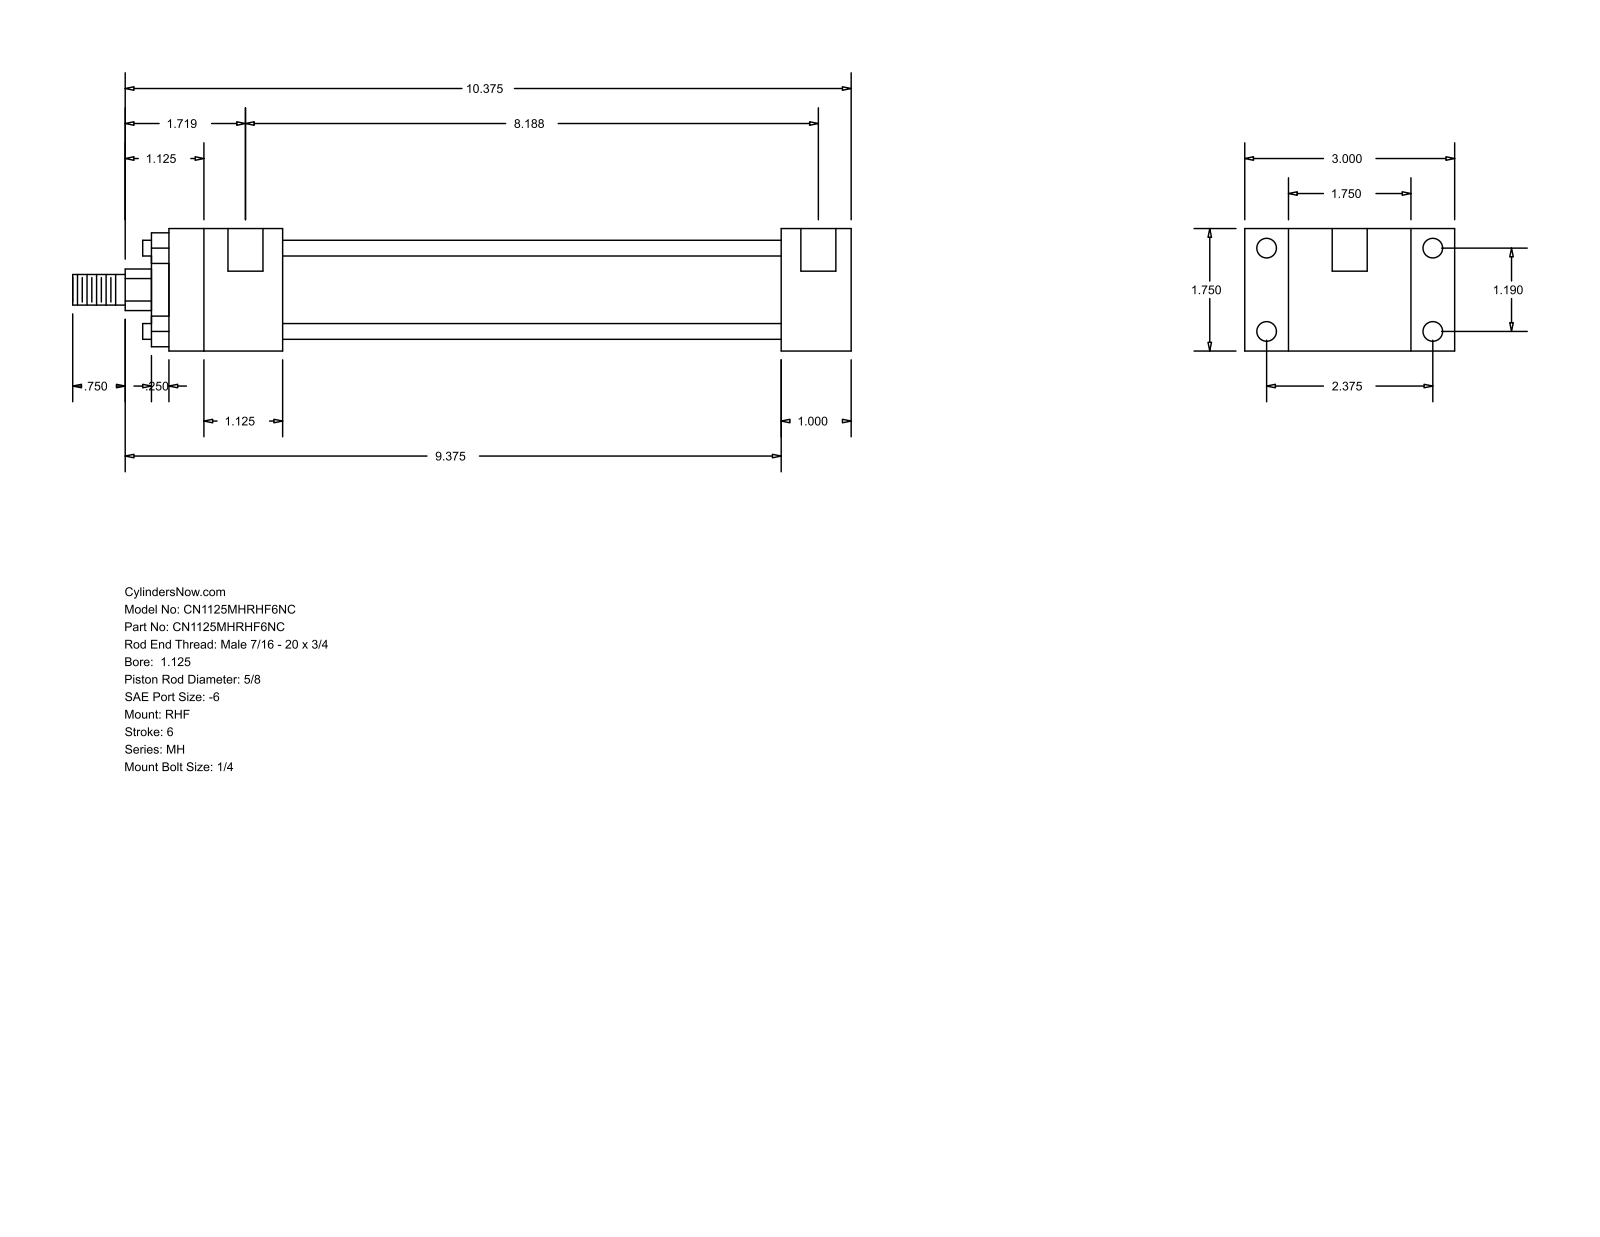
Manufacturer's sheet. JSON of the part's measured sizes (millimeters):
{"part_name": "MH_RHF__0112_0.625", "step_written_by": "GSSL Pune (CONFIG_CONTROL_DESIGN)", "units": "millimeters", "bodies": {"solids": 0, "faces": 88, "planar": 60, "cylindrical": 28, "other": 0}, "overall_size": [282.57, 76.2, 44.45], "round_holes": [[5.56, 4], [7.14, 4], [12.7, 2]], "round_bosses_or_shafts": [[5.71, 4], [34.92, 1], [28.57, 1], [15.88, 1], [11.11, 1]], "partial_cylinders_radius": [[7.54, 1]], "face_to_face_distances": [44.46, 15.87, 25.4, 60.33, 76.2, 180.97, 206.37, 41.27, 222.24, 247.64], "hole_center_spacings": [30.22, 60.32, 67.47, 204.79, 3.17, 207.96]}
